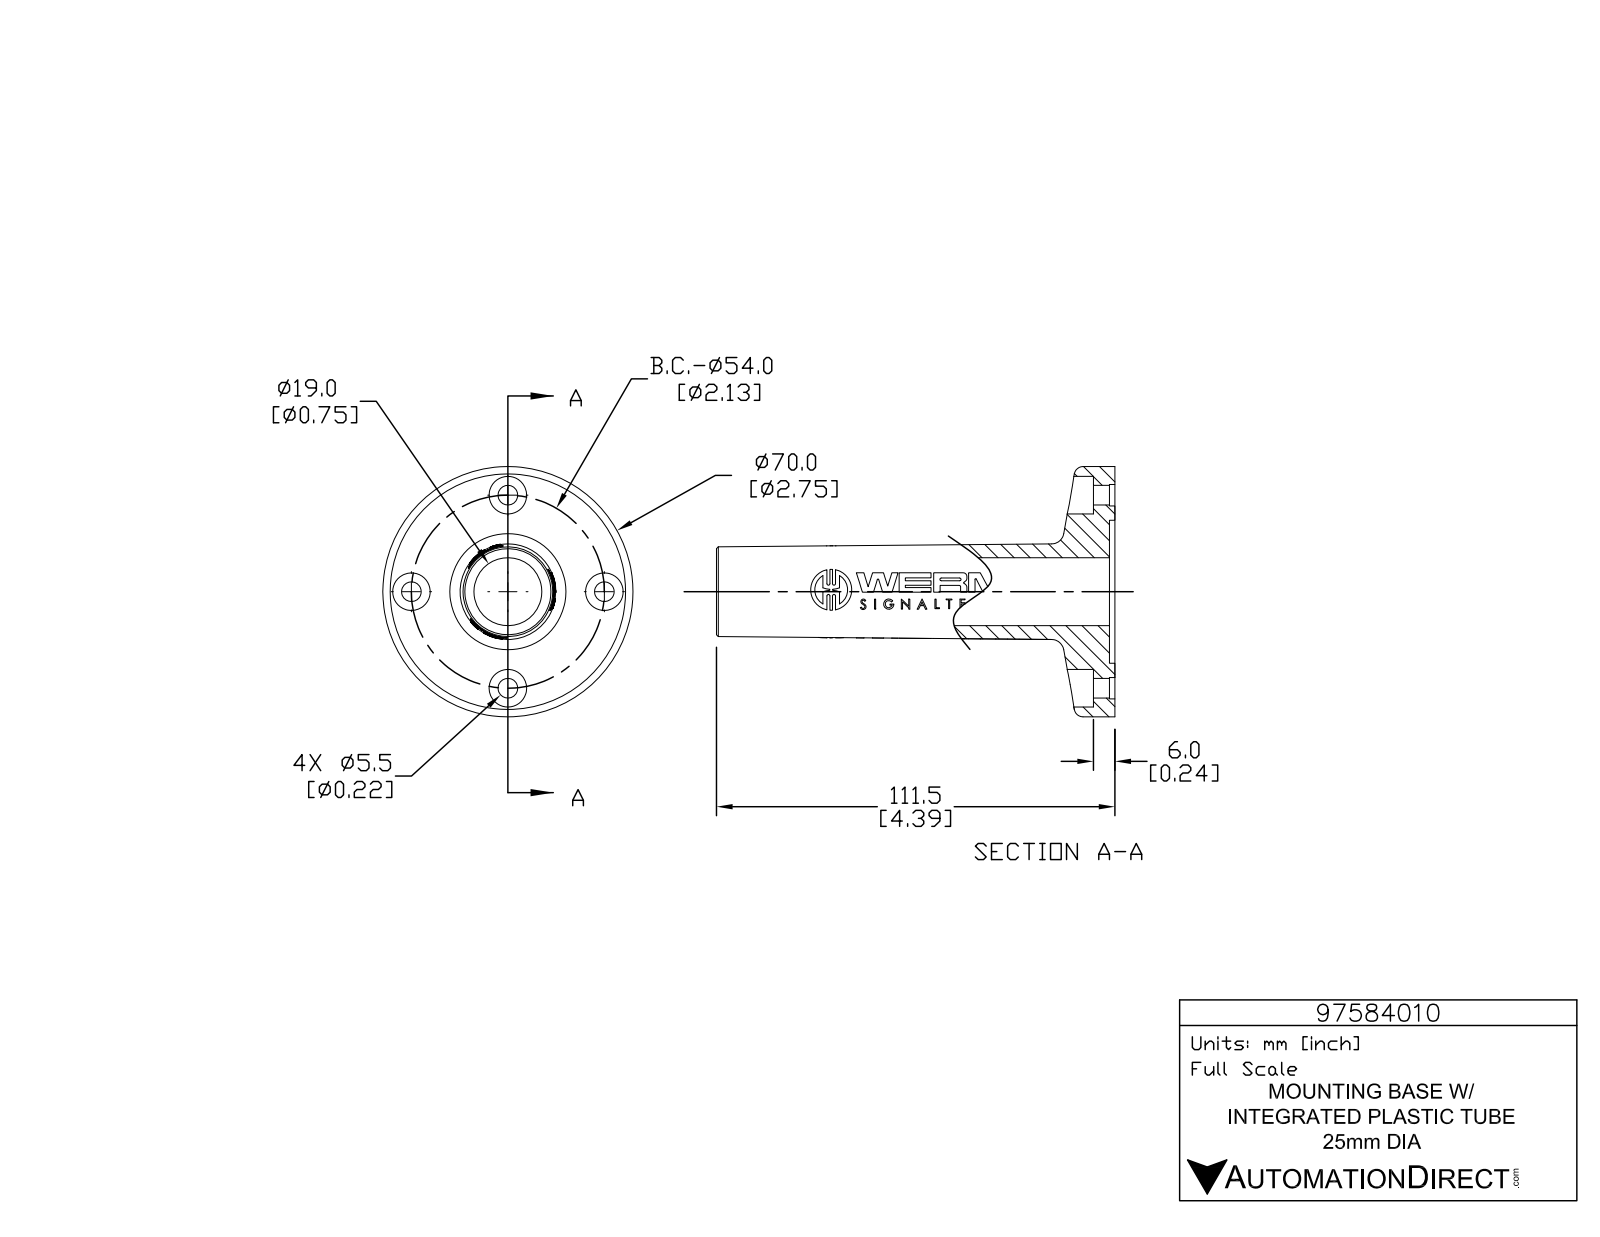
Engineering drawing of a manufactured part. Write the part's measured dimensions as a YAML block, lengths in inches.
part_name: "97584010"
step_written_by: "SolidWorks 2015 (AUTOMOTIVE_DESIGN)"
units: inches
bodies: {solids: 1, faces: 797, planar: 530, cylindrical: 180, other: 87}
overall_size: [4.39, 2.756, 2.756]
volume: 3.972
surface_area: 38.95
round_holes:
  - {diameter: 0.217, count: 4}
  - {diameter: 0.236, count: 4}
  - {diameter: 0.413, count: 4}
  - {diameter: 0.078, count: 3}
  - {diameter: 0.748, count: 1}
  - {diameter: 1.575, count: 1}
round_bosses_or_shafts:
  - {diameter: 0.452, count: 3}
  - {diameter: 0.113, count: 3}
  - {diameter: 2.756, count: 1}
partial_cylinders:
  - {radius: 0.007, count: 9}
  - {radius: 0.007, count: 6}
  - {radius: 0.016, count: 6}
  - {radius: 0.016, count: 6}
  - {radius: 0.016, count: 6}
  - {radius: 0.262, count: 6}
  - {radius: 0.006, count: 3}
  - {radius: 0.006, count: 3}
face_to_face_distances: [0.059, 0.177, 0.236, 4.154, 4.331, 4.39, 0.213, 0.075, 0.033, 0.061]
hole_center_spacings: [1.063, 1.503, 2.126]
